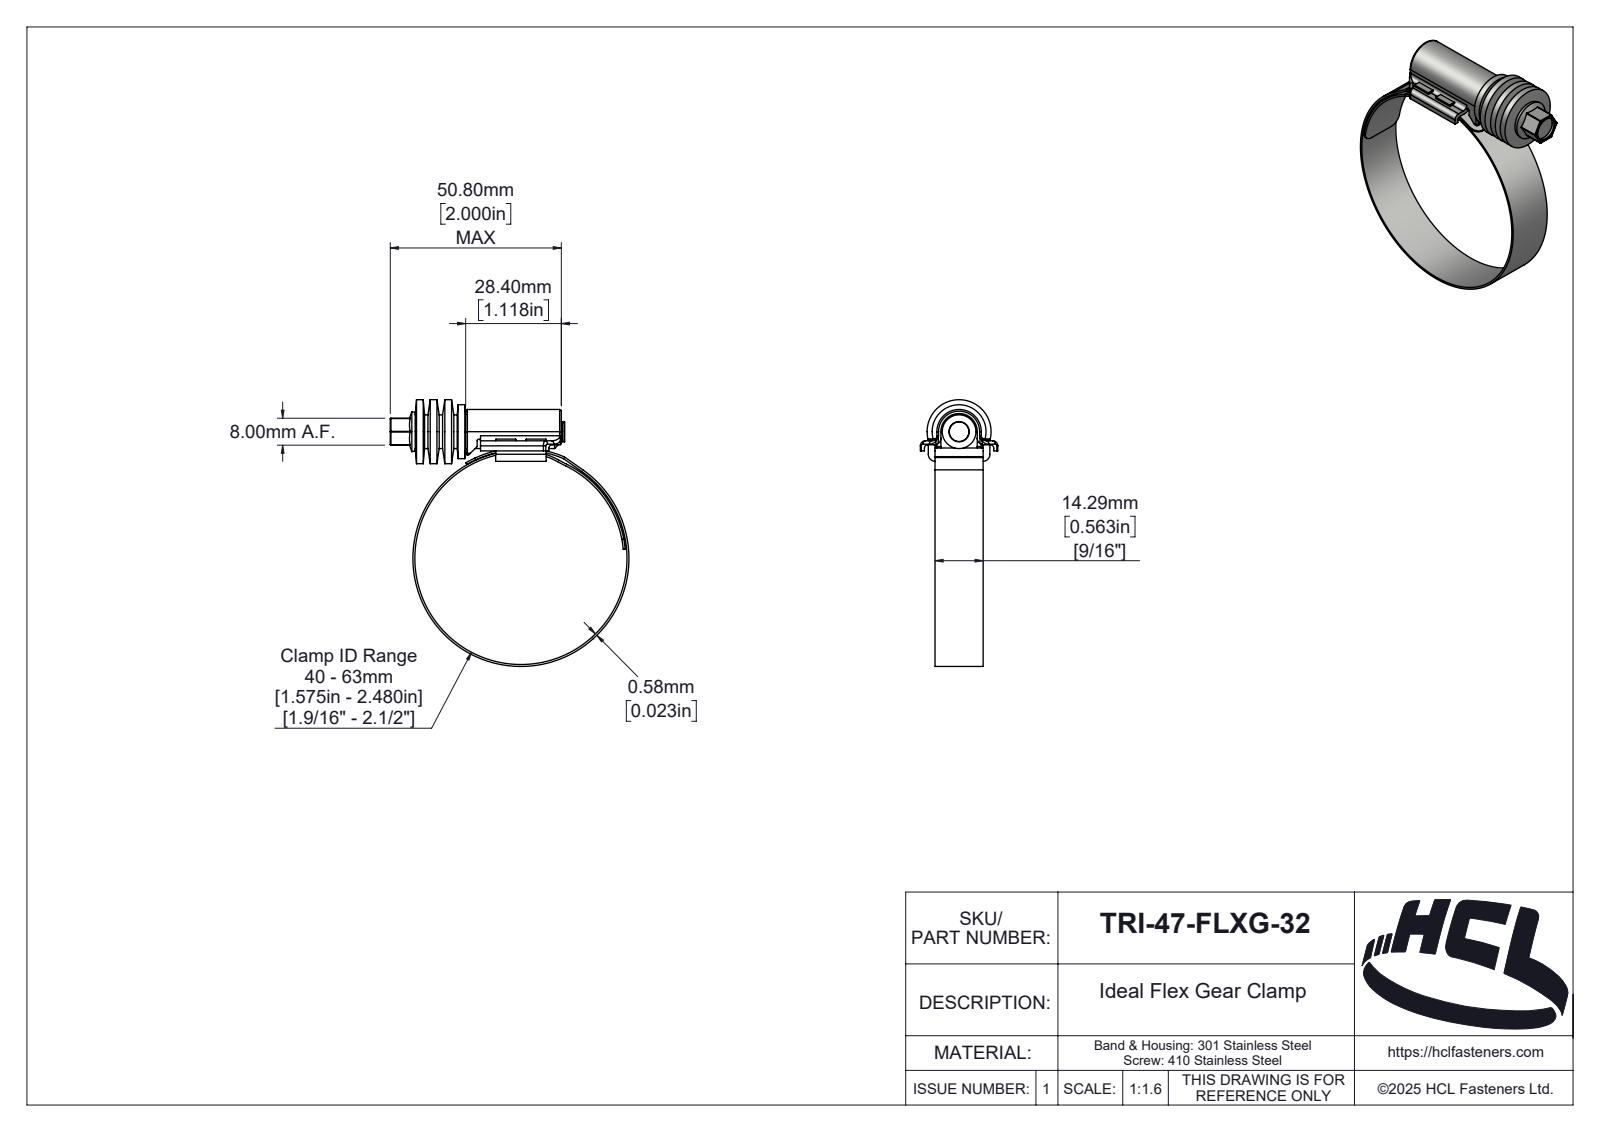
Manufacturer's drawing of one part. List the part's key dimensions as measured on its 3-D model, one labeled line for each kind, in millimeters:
Part name (STEP PRODUCT): TRI-47-FLXG-32
STEP written by: SolidWorks 2025 (AUTOMOTIVE_DESIGN)
Units: millimetres
Bodies: 4 solids, 323 faces (88 planar, 139 cylindrical, 96 other)
Overall size (bounding box): 79.18 × 70.88 × 23
Volume: 9 759 mm³ · Surface area: 14 272 mm²
Round holes (diameter × count): ⌀7 ×1, ⌀63 ×1
Round bosses / shafts (diameter × count): ⌀64.16 ×1, ⌀19 ×1, ⌀16 ×1, ⌀10 ×1, ⌀6 ×1, ⌀5 ×1
Partial cylindrical surfaces — rounded edges, fillets, slot ends (radius × count): R0.2 ×12, R0.5 ×9, R1 ×8, R1.5 ×4, R3 ×4, R2 ×3, R0.1 ×2, R2.1 ×2
Main face-to-face distances: 2, 1.2, 14.28, 4.9, 1.74, 12.54, 16.29, 6.1, 0.54, 13.74
